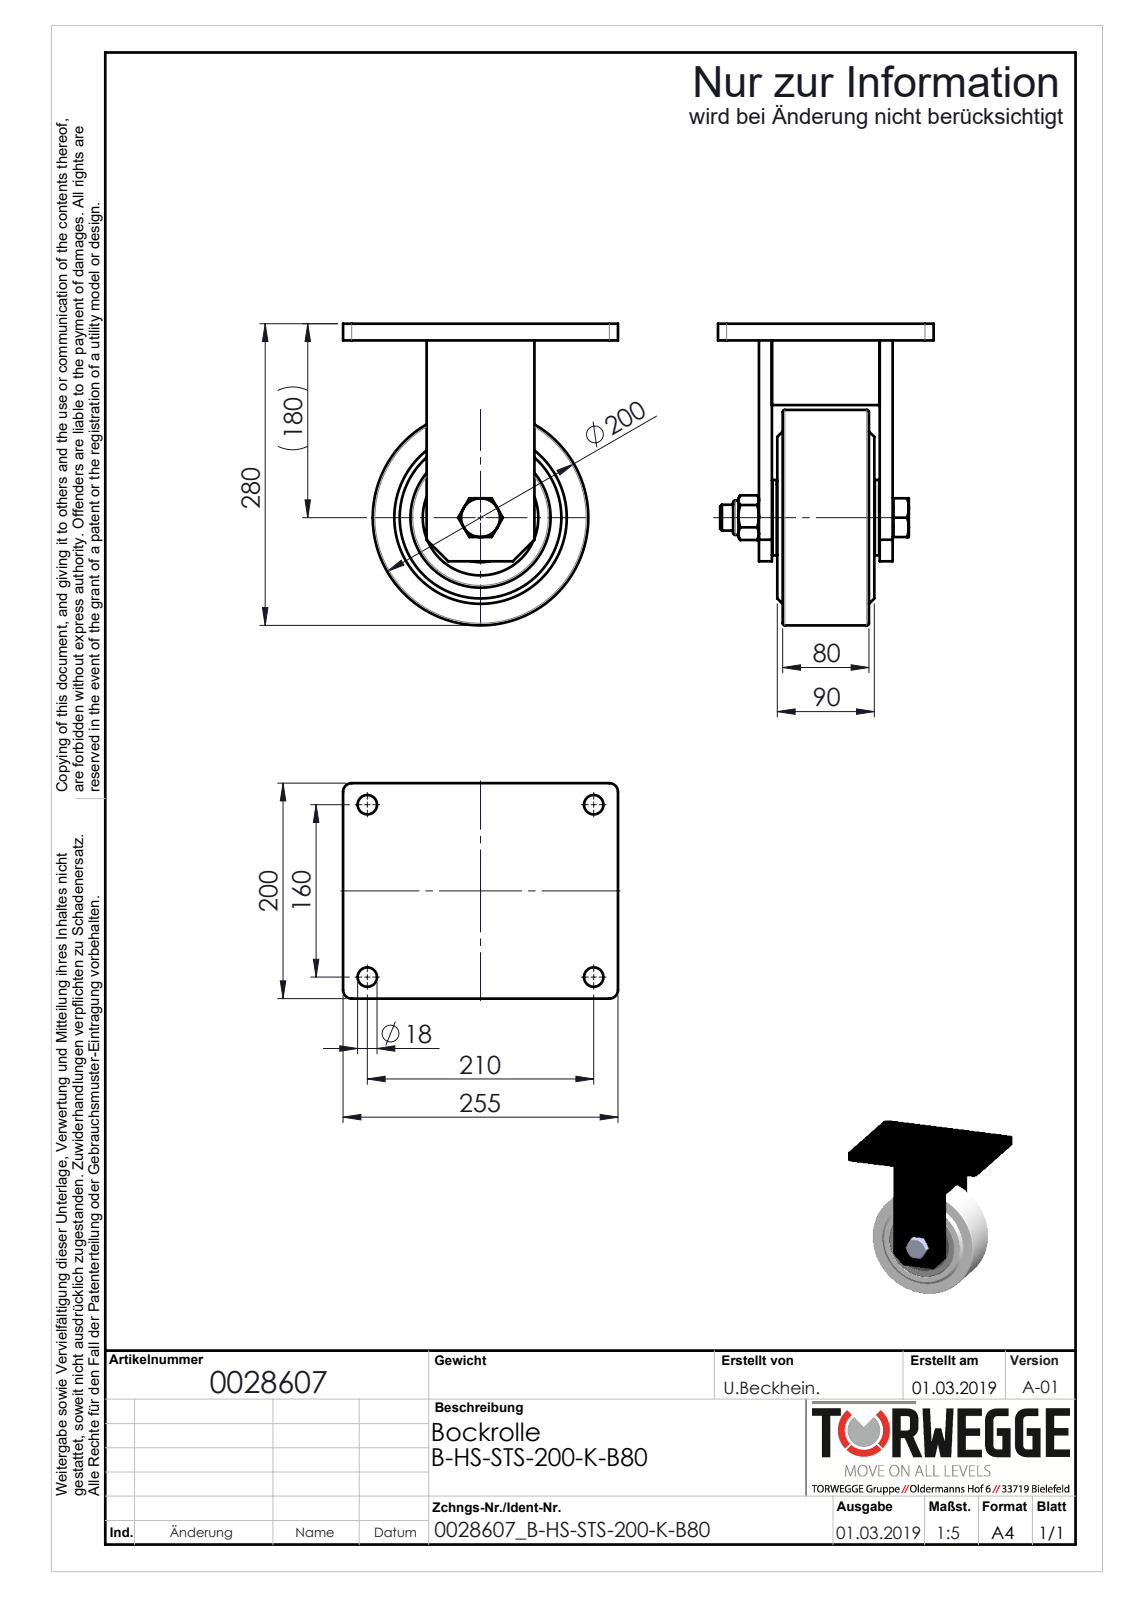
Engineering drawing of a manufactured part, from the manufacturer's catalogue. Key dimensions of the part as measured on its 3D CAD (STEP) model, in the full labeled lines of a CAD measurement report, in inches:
Part name (STEP PRODUCT): 0028607_B-HS-STS-200-K-B80_(A-01)
STEP written by: SolidWorks 2018 (AUTOMOTIVE_DESIGN)
Units: inches
Bodies: 0 solids, 204 faces (78 planar, 60 cylindrical, 66 other)
Overall size (bounding box): 11.024 × 10.039 × 7.874
Round holes (diameter × count): ⌀0.709 ×4, ⌀0.817 ×1, ⌀0.945 ×1, ⌀2.362 ×1, ⌀4.22 ×1, ⌀4.528 ×1, ⌀5.118 ×1
Round bosses / shafts (diameter × count): ⌀7.874 ×1, ⌀3.26 ×1, ⌀2.756 ×1, ⌀1.417 ×1, ⌀1.26 ×1
Partial cylindrical surfaces — rounded edges, fillets, slot ends (radius × count): R0.315 ×4
Main face-to-face distances: 0.472, 0.61, 0.197, 4.409, 3.543, 3.937, 0.669, 4.213, 3.74, 4.882
Hole centre spacings: 6.299, 8.268, 10.394
